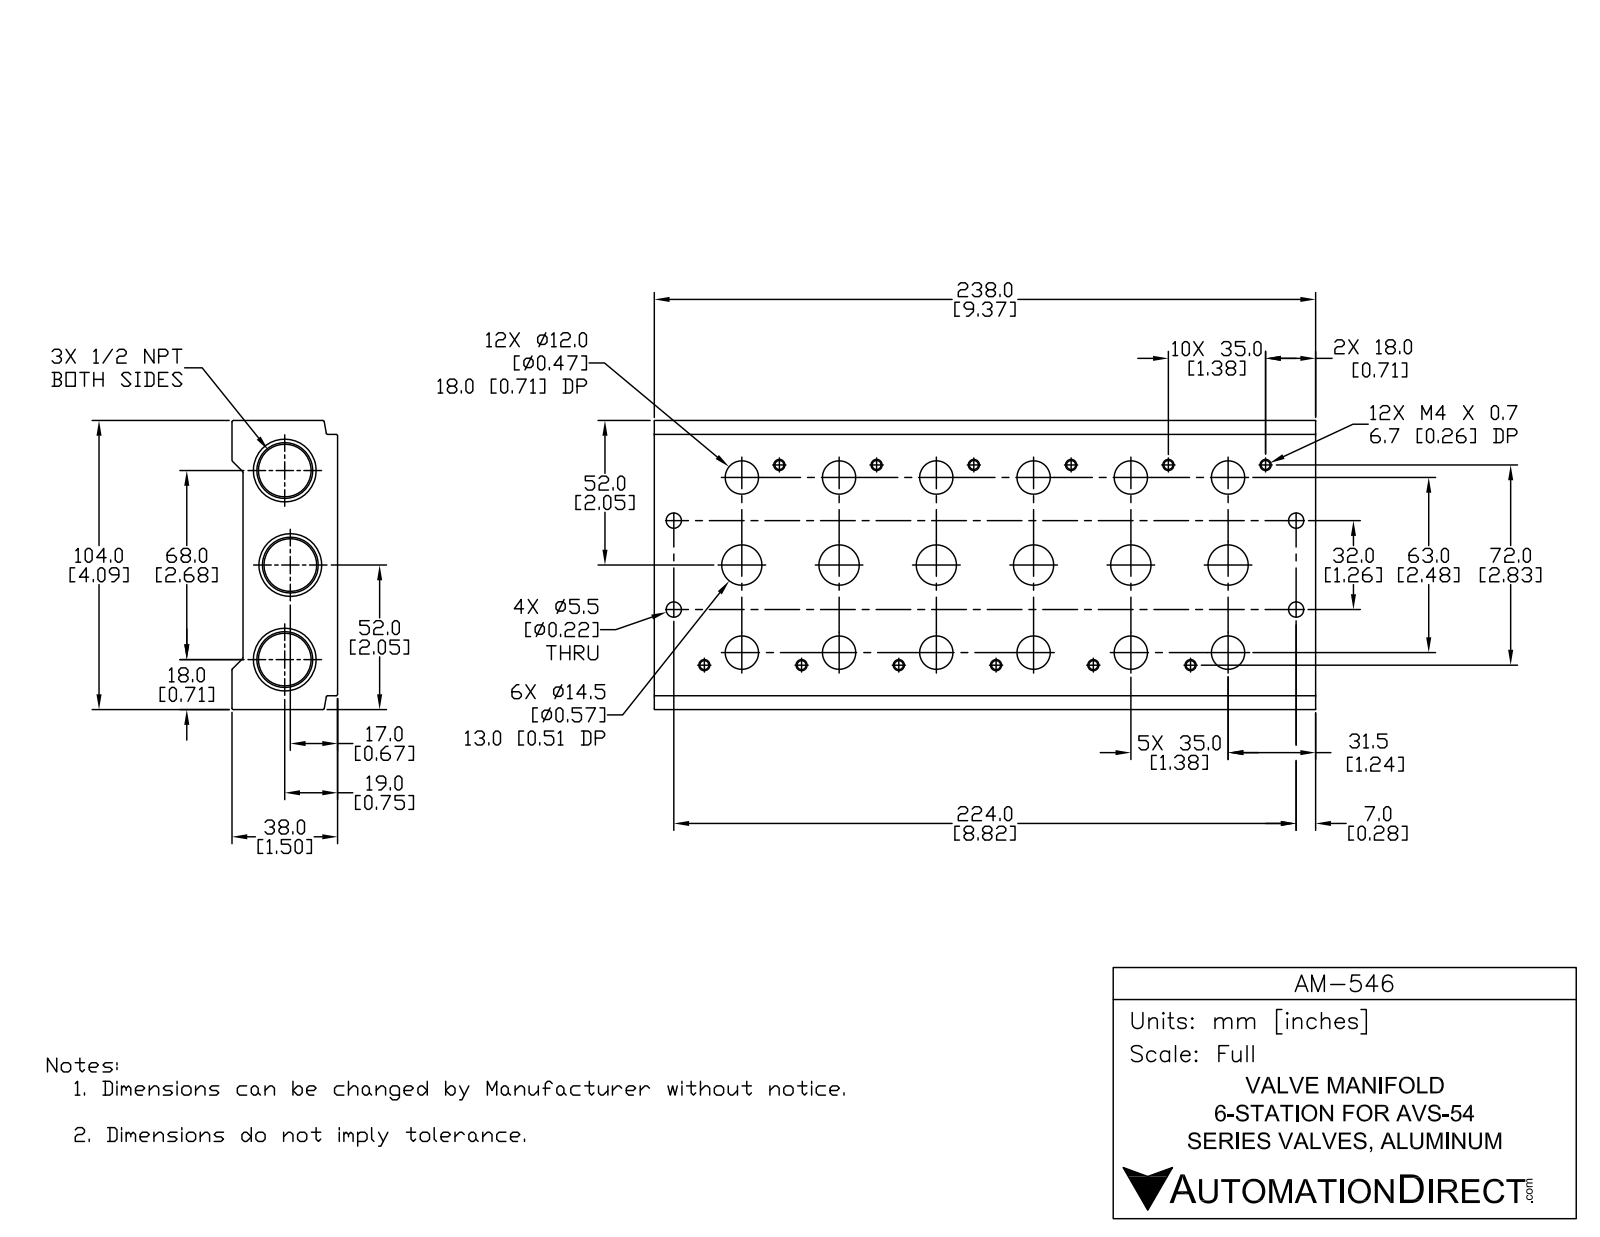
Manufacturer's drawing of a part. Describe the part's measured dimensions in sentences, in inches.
The part is named "AM-546". Its 3-D file was written by "SolidWorks 2015 (CONFIG_CONTROL_DESIGN)". It is 1 solid with 165 faces: 44 planar, 85 cylindrical and 36 other. Overall it measures 9.37 by 4.094 by 1.496 inches. Its volume is 41.6 cubic inches and its surface area 187.7 square inches. Round holes: 12 of diameter 0.13, 12 of diameter 0.335, 6 of diameter 0.512, 4 of diameter 0.217, 3 of diameter 0.703. Partial cylindrical surfaces (rounded edges, fillets, slot ends): 11 of radius 0.02. The main face-to-face distances are 1.496, 0.157, 1.339, 4.094, 9.37, 1.102, 0.945, 0.394, 0.236, 3.858. The hole center spacings are 1.378, 1.854, 2.756, 4.134, 0.56, 1.24, 1.514, 2.71.
